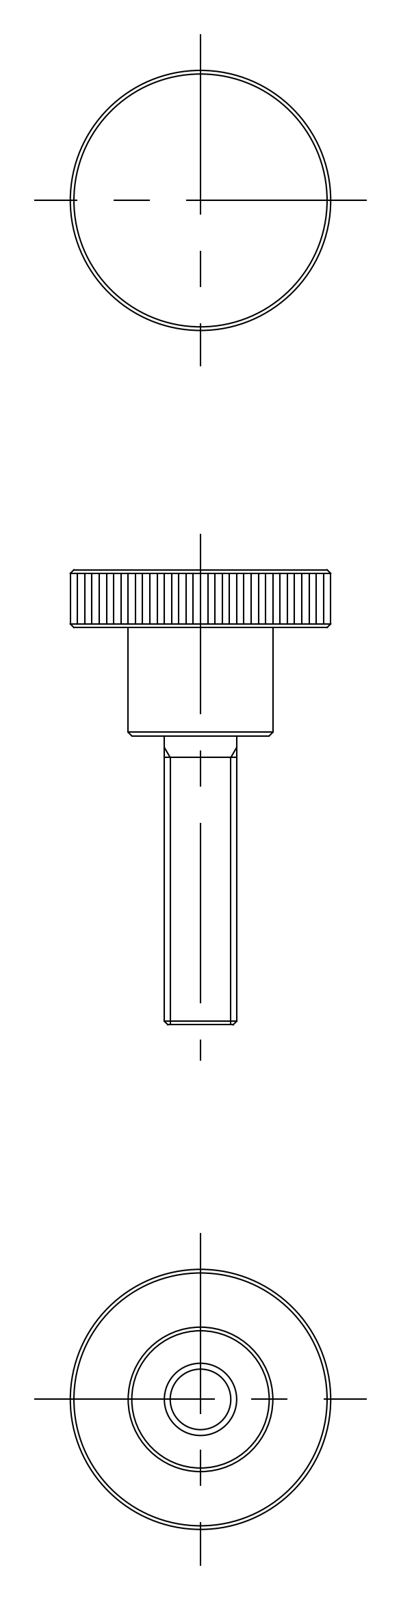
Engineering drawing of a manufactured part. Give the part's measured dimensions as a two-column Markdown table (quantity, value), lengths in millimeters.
| quantity | value |
| --- | --- |
| part name | knob |
| STEP written by | CADfix (AUTOMOTIVE_DESIGN) |
| units | millimeters |
| bodies | 1 solid, 18 faces (0 planar, 0 cylindrical, 18 other) |
| overall size | 63 × 36 × 36 |
| volume | 15 987 mm³ |
| surface area | 5 046 mm² |
